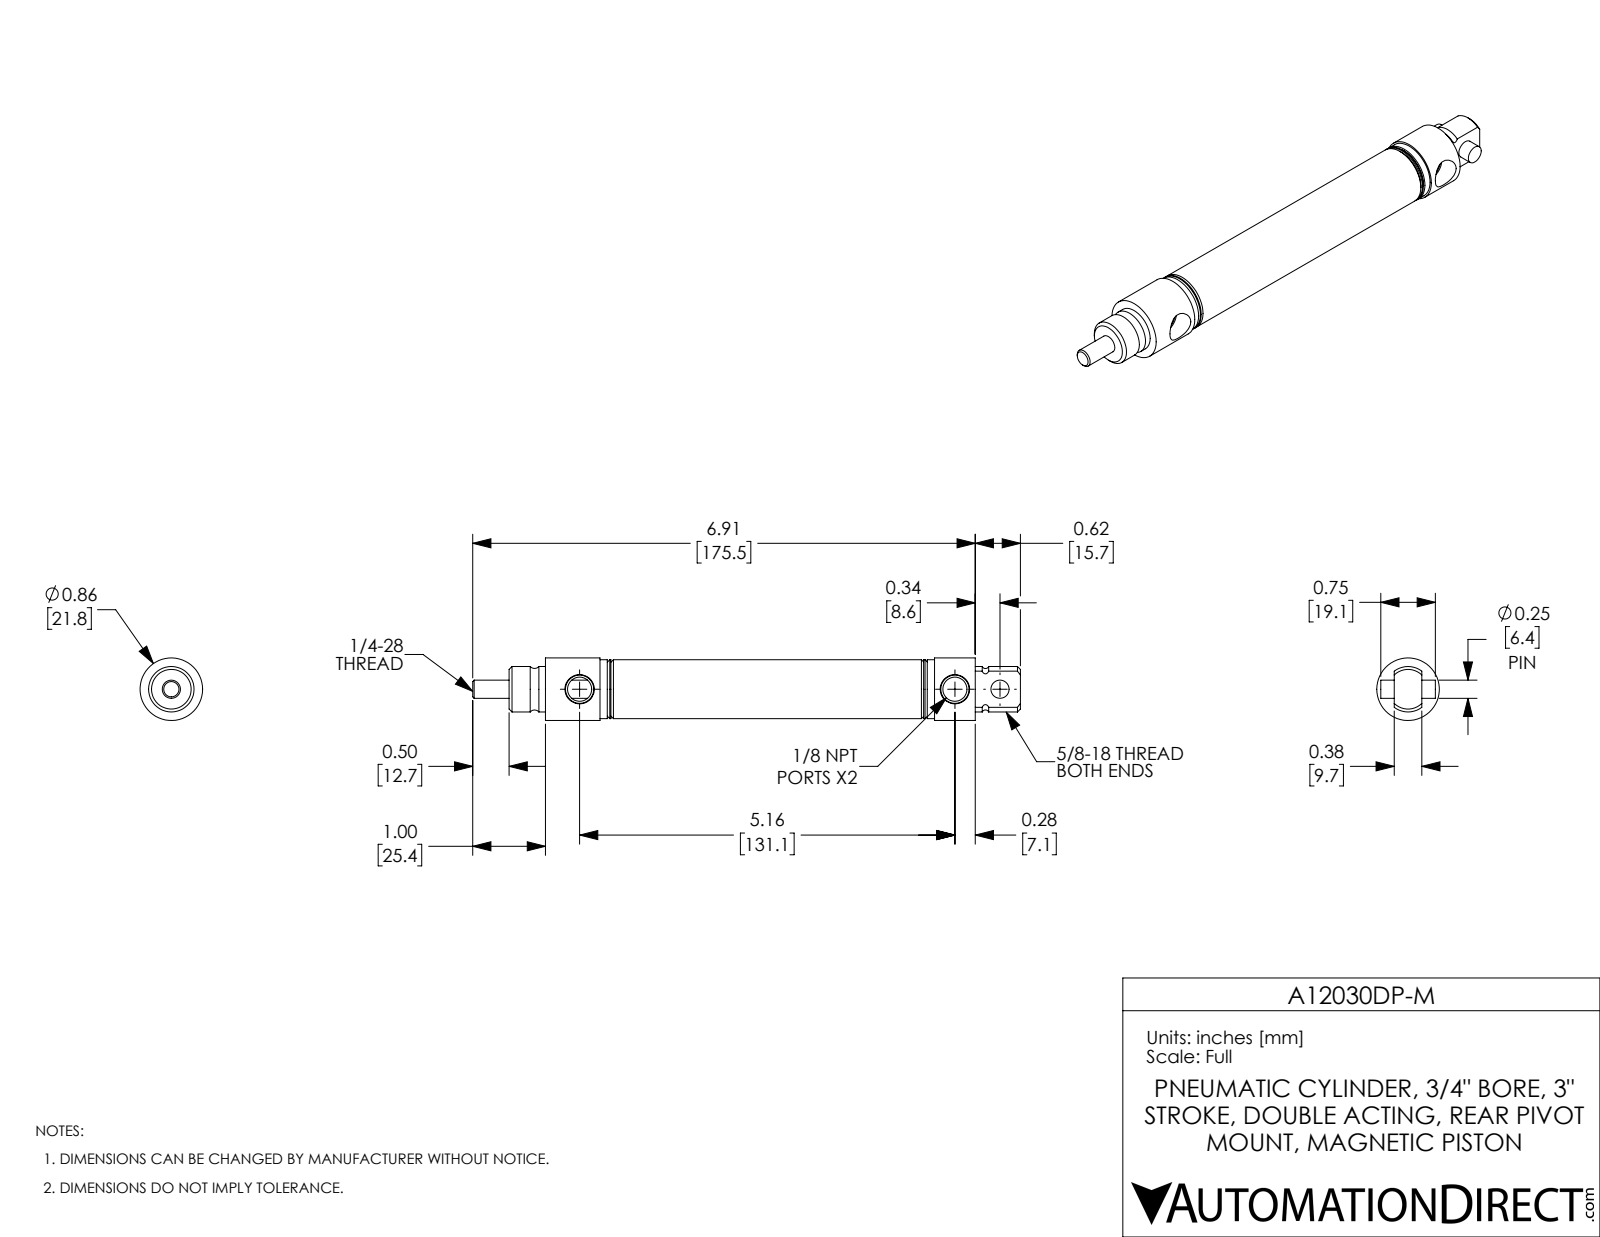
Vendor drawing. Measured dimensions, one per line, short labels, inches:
name: A12030DP-M-MainBody; A12030DP-M-Rod; A12030DP-M-PIN; A12030DP-M
written by: SolidWorks 2017 (AUTOMOTIVE_DESIGN)
unit: in
bodies: 3 solids, 91 faces (21 planar, 38 cylindrical, 32 other)
size: 7.53 × 0.86 × 0.86
volume: 2.184 in³; area: 37.15 in²
holes: 2× ⌀0.25, 2× ⌀0.332, 1× ⌀0.75
bosses: 1× ⌀0.86, 1× ⌀0.81, 1× ⌀0.625
face distances: 0.5, 4.705, 3.5, 3, 1.205, 1.705, 4.705, 5.91, 4.205, 1.205
hole spacings: 0.62, 5.16, 5.78
